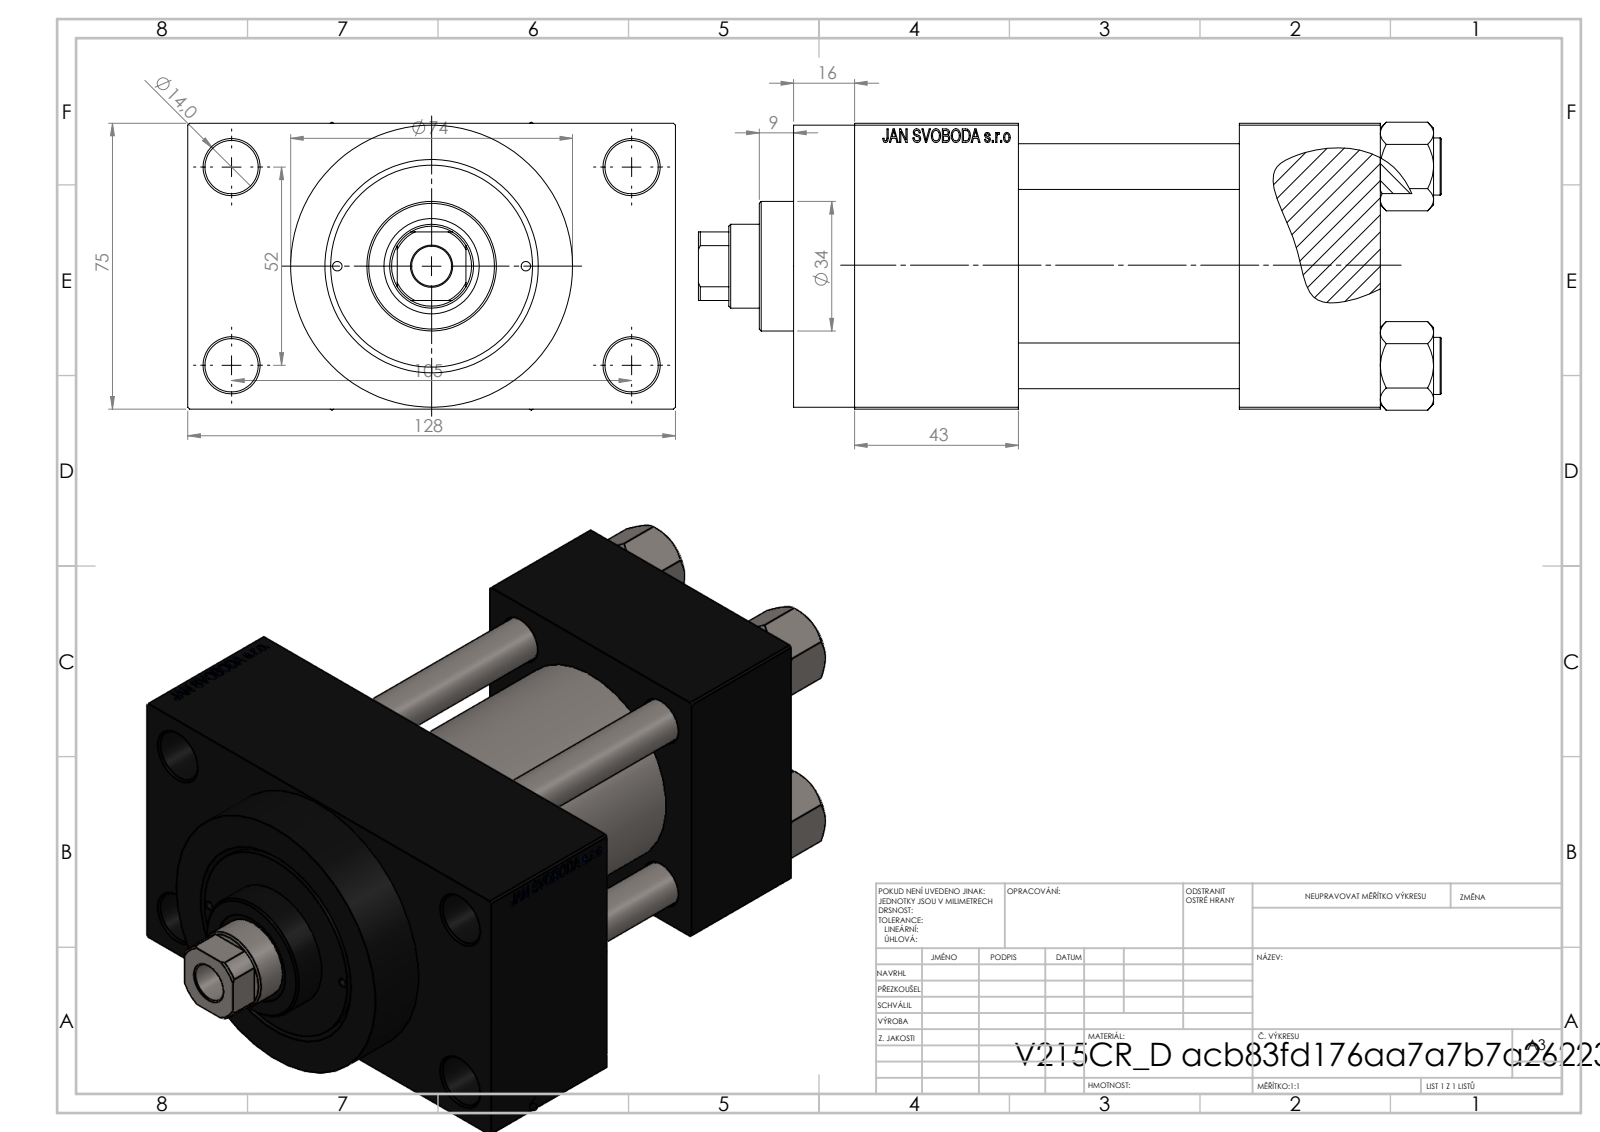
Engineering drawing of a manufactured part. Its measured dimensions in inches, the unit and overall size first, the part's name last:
Units: inches
Overall size (bounding box): 7.677 × 5.039 × 2.974
Round holes (diameter × count): ⌀0.472 ×4, ⌀0.551 ×4, ⌀0.098 ×2, ⌀0.276 ×2, ⌀0.825 ×2, ⌀1.181 ×2, ⌀0.413 ×1, ⌀0.866 ×1, ⌀0.984 ×1, ⌀1.614 ×1, ⌀1.969 ×1, ⌀2.087 ×1
Round bosses / shafts (diameter × count): ⌀0.591 ×4, ⌀2.913 ×1, ⌀2.205 ×1, ⌀1.339 ×1
Partial cylindrical surfaces — rounded edges, fillets, slot ends (radius × count): R0.413 ×1
Main face-to-face distances: 2.953, 2.283, 1.457, 3.74, 1.043, 5.433, 3.976, 1.693, 3.996, 0.63
Hole centre spacings: 1.031, 1.037, 1.456, 1.497, 2.059, 2.253, 2.3, 2.307
Volume: 48.65 in³ · Surface area: 258.3 in²
Bodies: 11 solids, 1111 faces (499 planar, 92 cylindrical, 520 other)
Part name (STEP PRODUCT): V215_VC_A; V215CR_D_Body; NUT_M5_D; V215CR_D_TYCINKA (+1 more)
STEP written by: SolidWorks 2019 (CONFIG_CONTROL_DESIGN)
